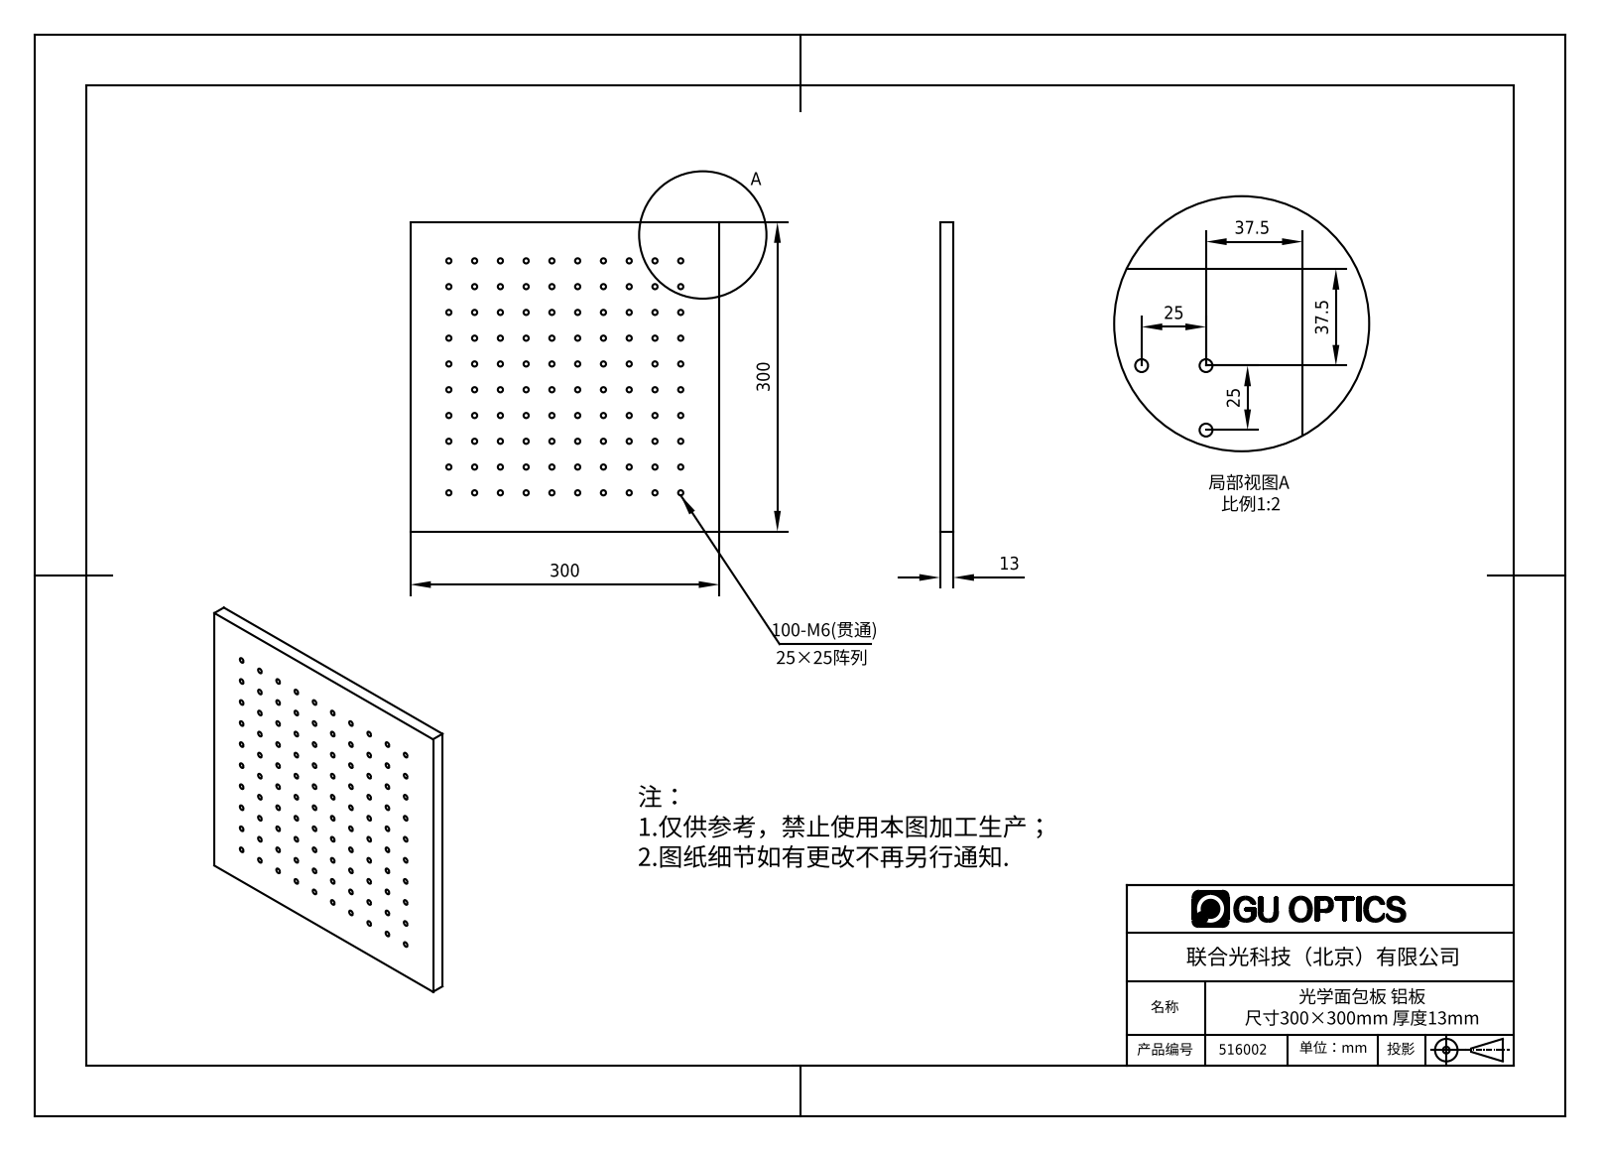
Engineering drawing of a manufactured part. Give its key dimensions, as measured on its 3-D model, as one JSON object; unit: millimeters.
{"part_name": "516002", "step_written_by": "SolidWorks 2016 (AUTOMOTIVE_DESIGN)", "units": "millimeters", "bodies": {"solids": 1, "faces": 206, "planar": 6, "cylindrical": 200, "other": 0}, "overall_size": [300, 300, 13], "volume_mm3": 1144000, "surface_area_mm2": 212093, "round_holes": [[5, 100]], "face_to_face_distances": [13, 300], "hole_center_spacings": [55.9, 25, 35.36, 79.06, 50, 90.14, 103.08, 75]}
